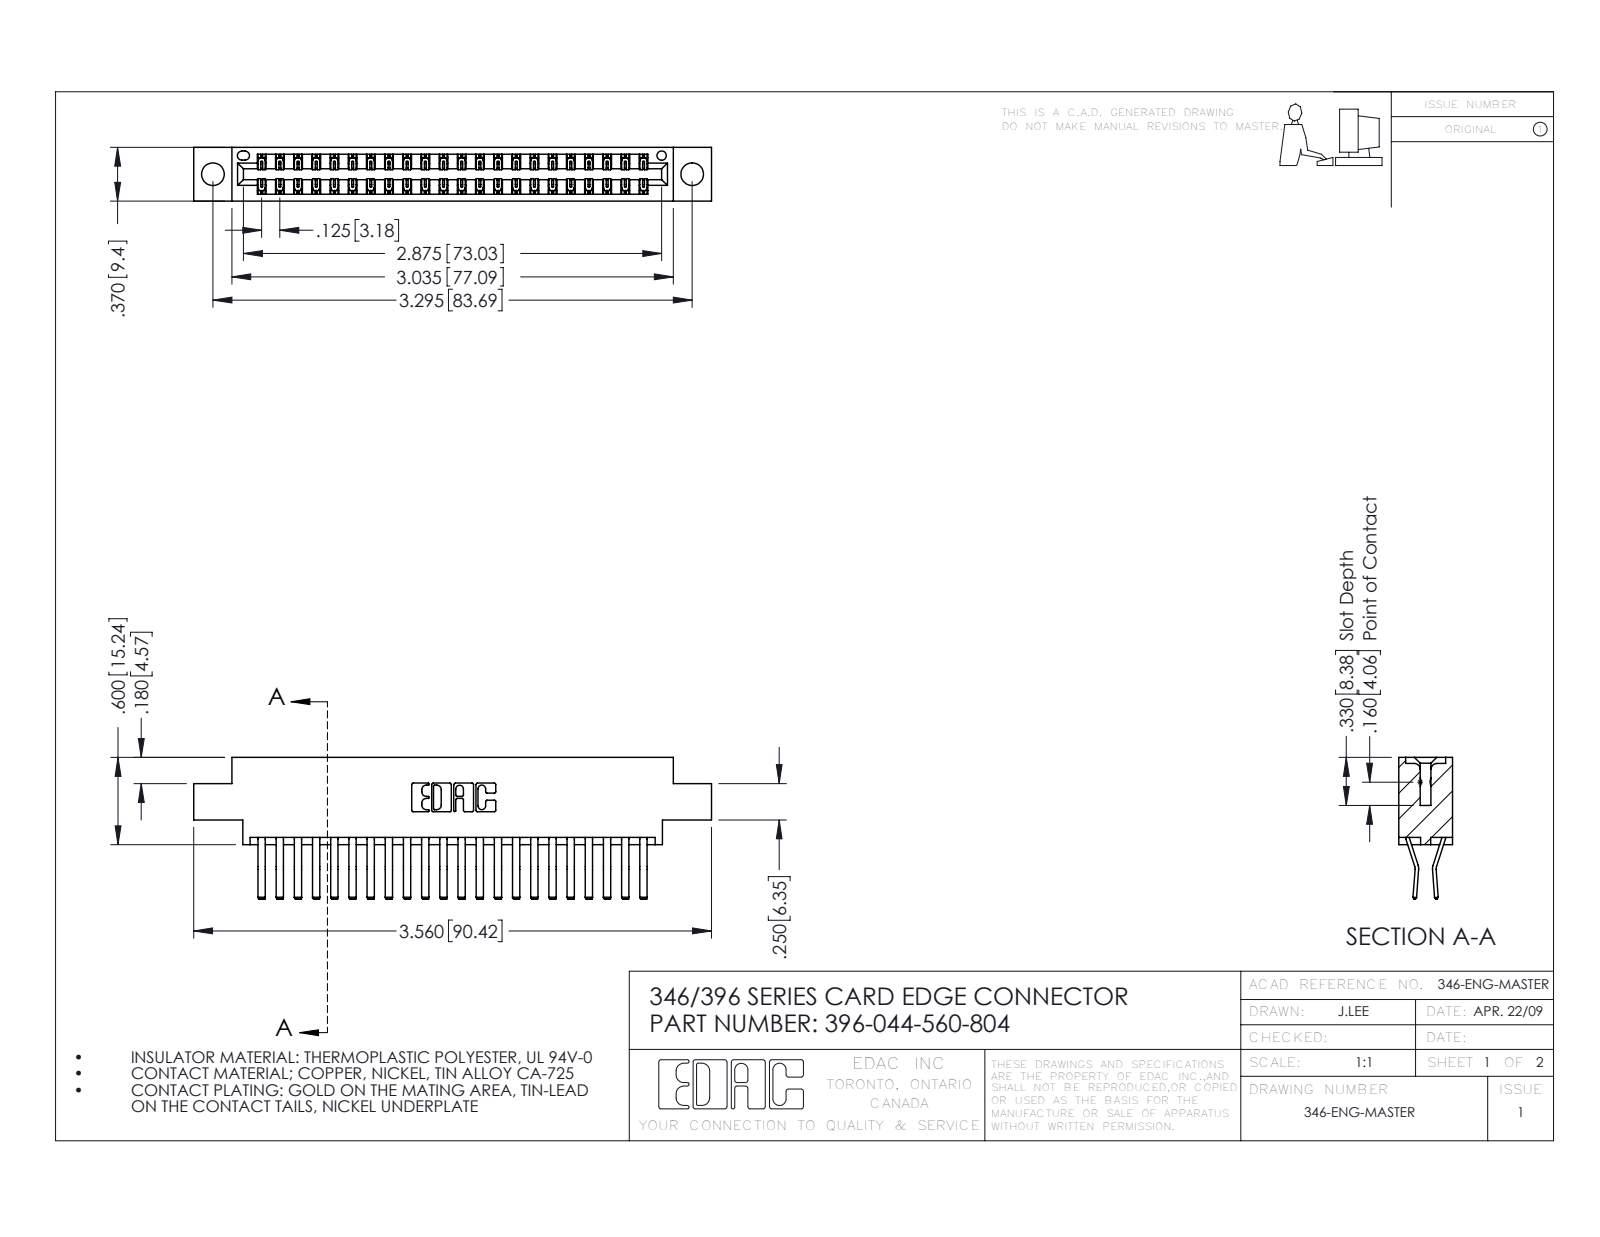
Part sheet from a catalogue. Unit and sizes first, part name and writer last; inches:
Units: inches
Overall size (bounding box): 3.56 × 0.975 × 0.37
Round holes (diameter × count): ⌀0.156 ×2, ⌀0.064 ×1
Partial cylindrical surfaces — rounded edges, fillets, slot ends (radius × count): R0.006 ×66, R0.01 ×22, R0.007 ×6, R0.031 ×6, R0.026 ×3, R0.01 ×2, R0.014 ×2, R0.022 ×2
Main face-to-face distances: 0.048, 0.322, 0.37, 0.25, 0.025, 0.072, 0.298, 0.275, 0.148, 0.222
Hole centre spacings: 0.246, 3.087, 3.295
Volume: 0.531 in³ · Surface area: 19.25 in²
Bodies: 45 solids, 2502 faces (1620 planar, 882 cylindrical, 0 other)
Part name (STEP PRODUCT): 345-292-001_560 Tail; 346 Part_0.170 Offset - 0.156 Dia-TH; 396-044-560-804
STEP written by: SolidWorks 2016 (CONFIG_CONTROL_DESIGN)
